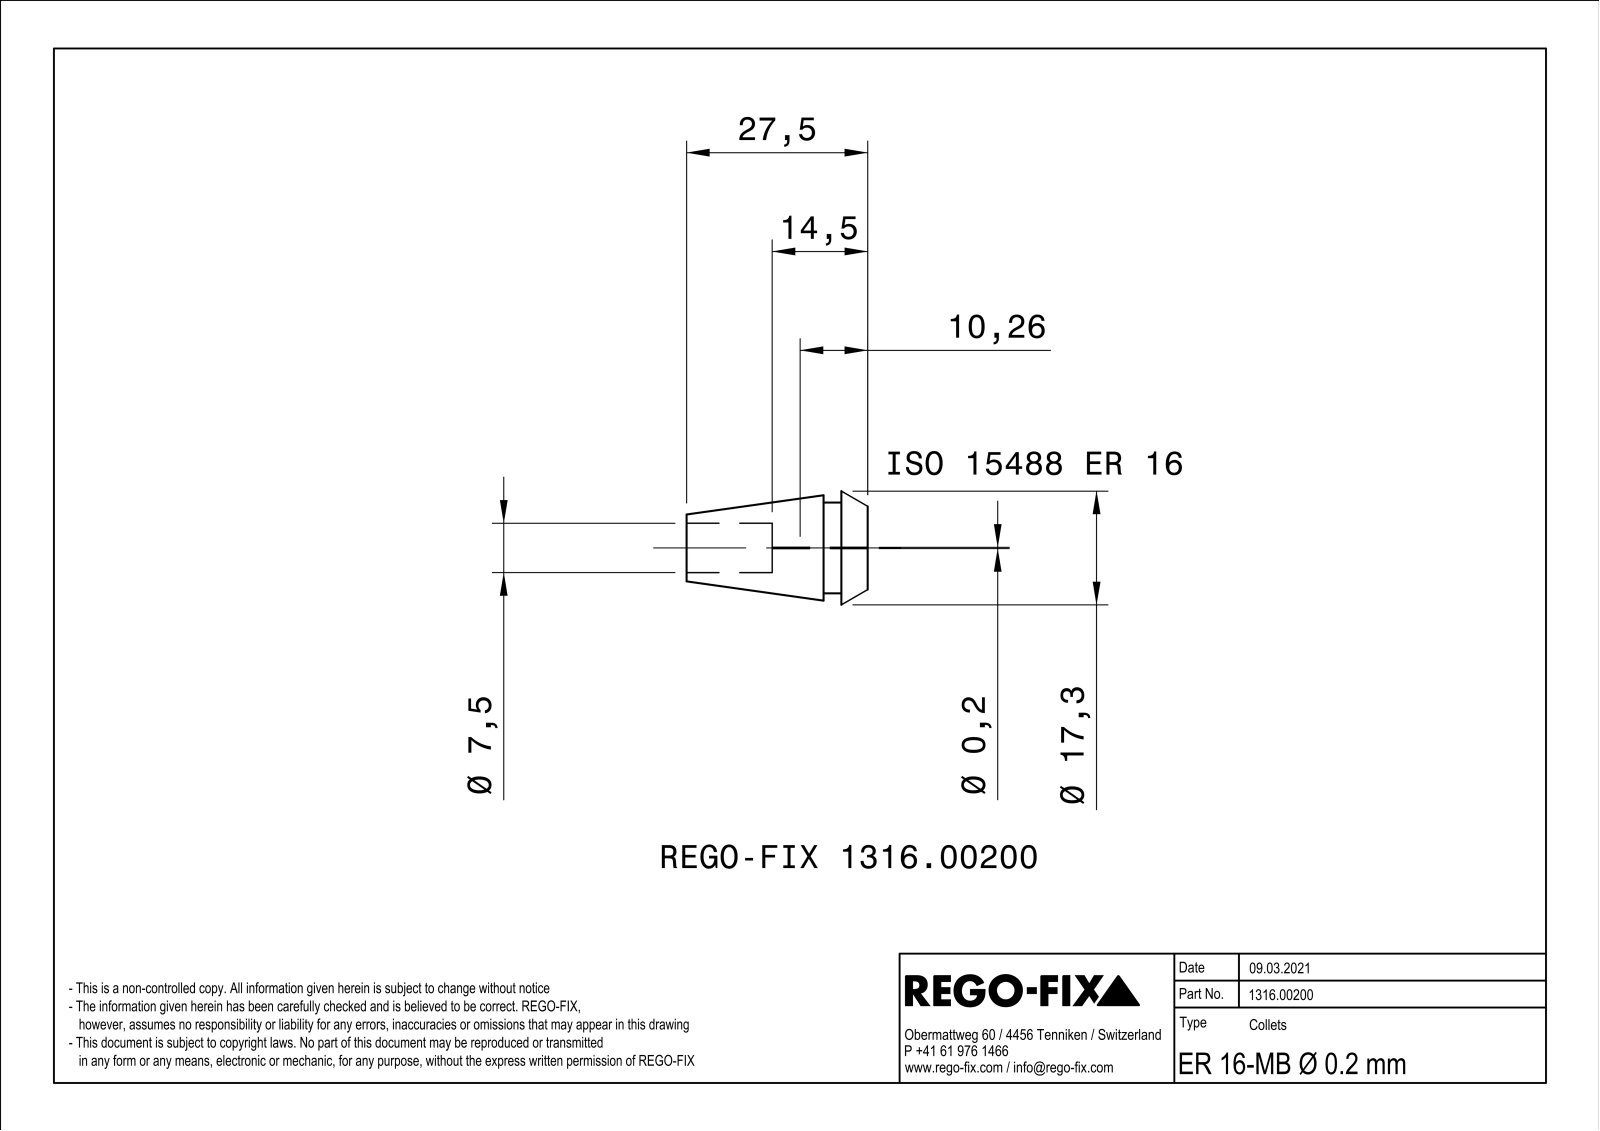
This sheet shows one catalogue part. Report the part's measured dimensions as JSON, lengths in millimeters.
{"part_name": "NOCUT", "step_written_by": "SIEMENS PLM Software Solid Edge ST10 (AUTOMOTIVE_DESIGN)", "units": "millimeters", "bodies": {"solids": 1, "faces": 69, "planar": 29, "cylindrical": 13, "other": 27}, "overall_size": [27.5, 17.25, 17.25], "volume_mm3": 2972, "surface_area_mm2": 2768, "round_holes": [[2, 3], [7.5, 1]], "round_bosses_or_shafts": [[13.8, 1]], "partial_cylinders_radius": [[0.1, 1]], "face_to_face_distances": [0.8, 0.34, 0.46, 4, 6.7, 2.7, 27.5, 23.5, 20.8, 14.5], "hole_center_spacings": [2.1, 3.64]}
